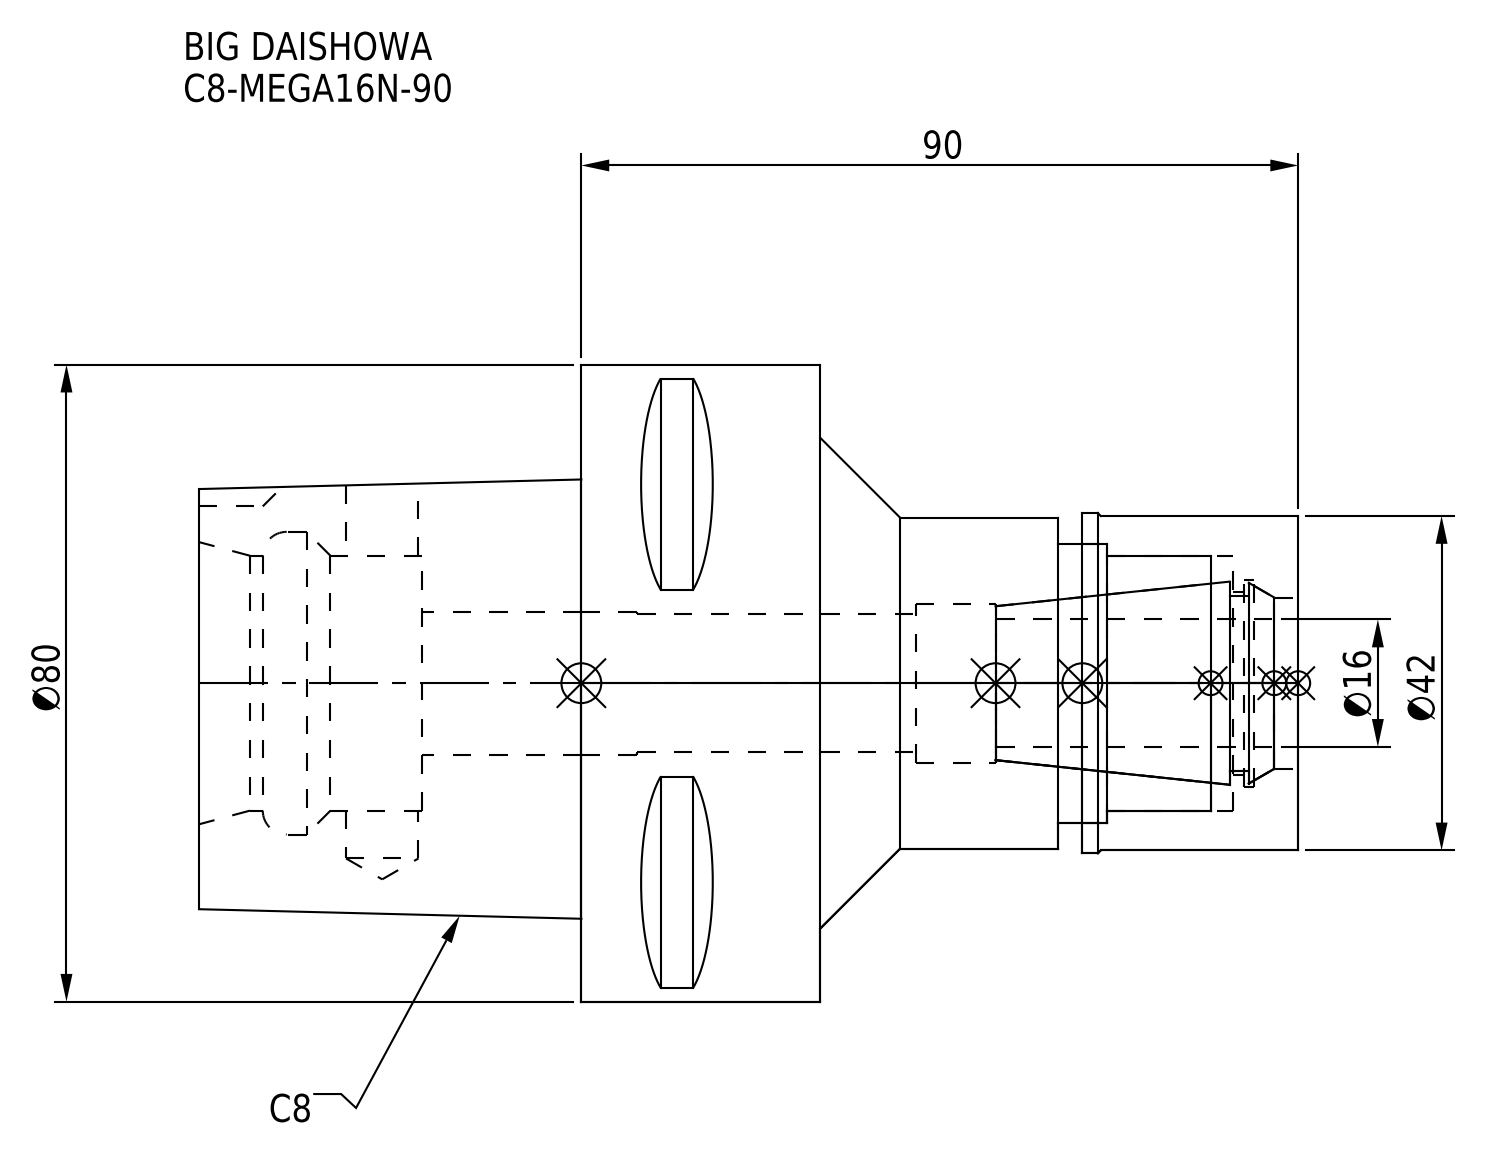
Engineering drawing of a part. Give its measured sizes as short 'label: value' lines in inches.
name: DXF_TEMP_ASSY_ASM_4_ASM.stp; MGN16_1.stp; C8-MEGA16N-90-160_ASM.stp; C8-MEGA16N-90_1.stp (+3 more)
written by: SolidWorks 2019 (CONFIG_CONTROL_DESIGN)
unit: in
bodies: 2 solids, 95 faces (38 planar, 39 cylindrical, 18 other)
size: 5.433 × 3.15 × 3.15
volume: 17.36 in³; area: 75.08 in²
holes: 1× ⌀0.358, 1× ⌀0.681, 1× ⌀0.709, 1× ⌀0.787, 1× ⌀0.846, 1× ⌀0.906, 1× ⌀1.024, 1× ⌀1.26, 1× ⌀1.378, 1× ⌀1.496
bosses: 1× ⌀3.15, 1× ⌀1.681, 1× ⌀1.654, 1× ⌀1.638
rounds: 1× R0.236
face distances: 1.181, 1.89, 3.543, 3.071, 2.362, 5.433, 0.787, 4.331, 1.969, 1.102
